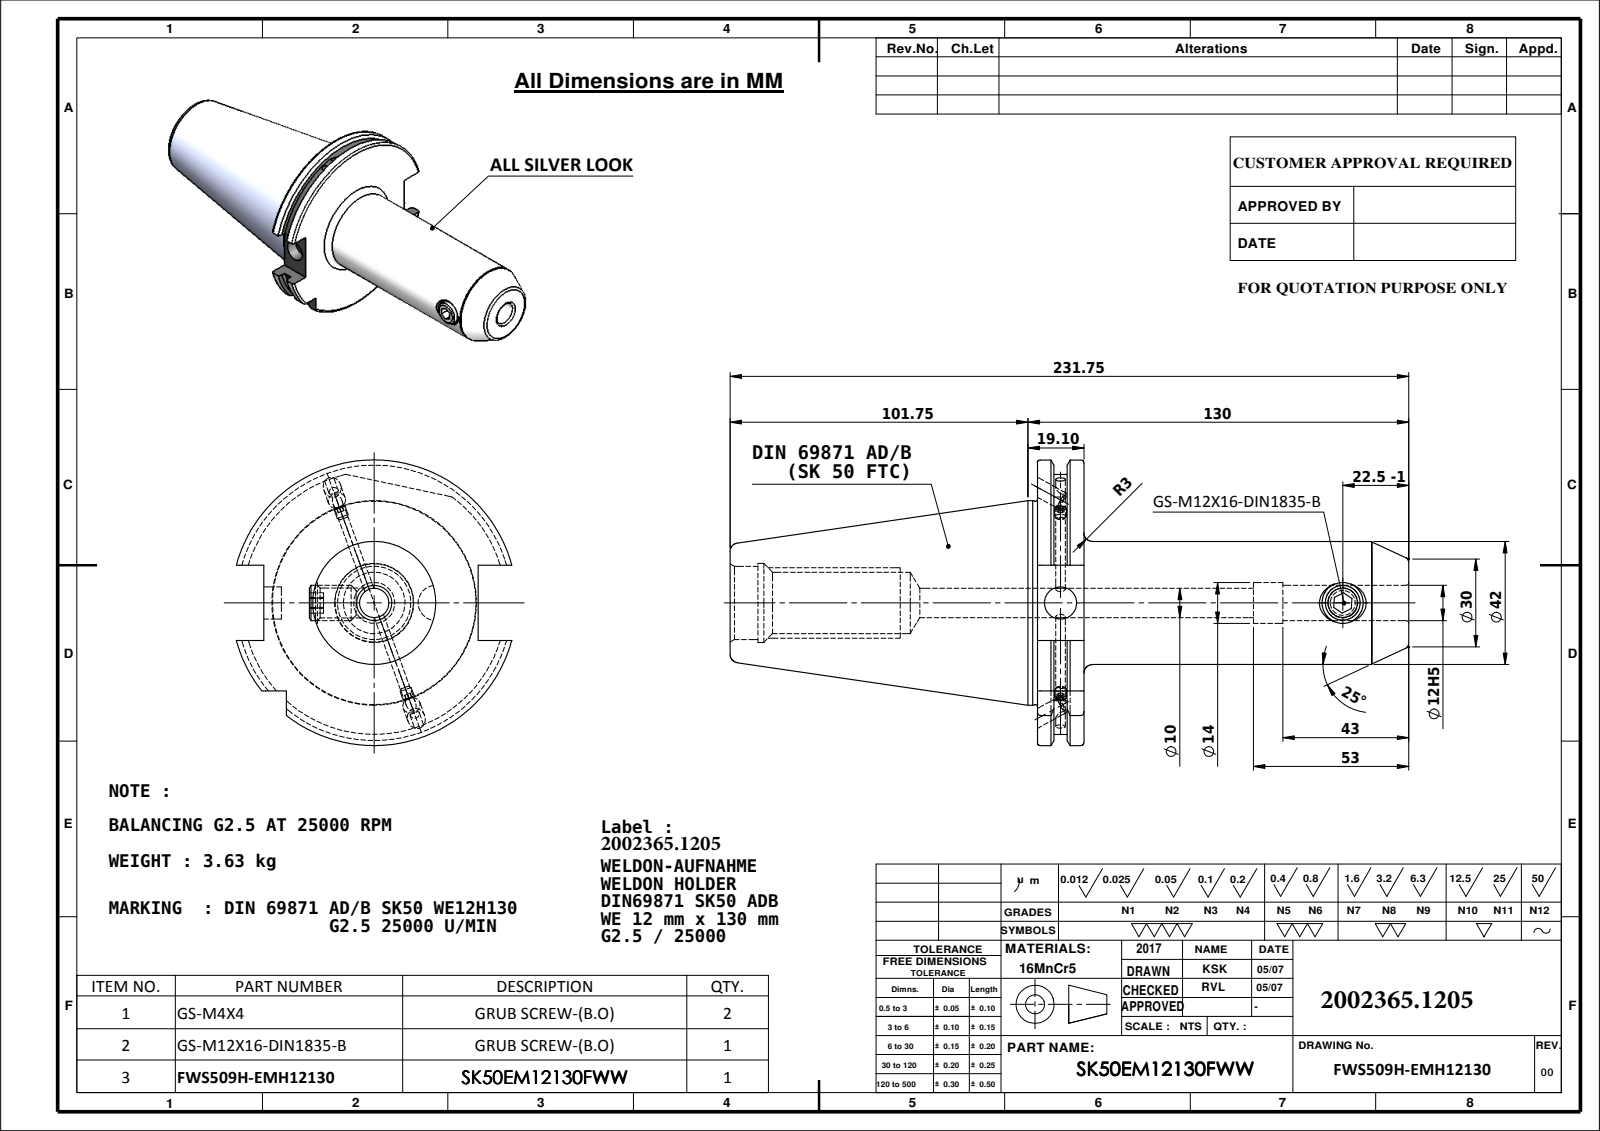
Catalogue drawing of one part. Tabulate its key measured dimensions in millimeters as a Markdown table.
| quantity | value |
| --- | --- |
| part name | SK50EM12130FWW; 91506-WE712130; Copy of M4X4_DIN 913 - M4 x 4-N; M12X16_ISO 4026 - M12 x 12-N |
| STEP written by | SolidWorks 2009 (CONFIG_CONTROL_DESIGN) |
| units | millimeters |
| bodies | 4 solids, 168 faces (53 planar, 55 cylindrical, 60 other) |
| overall size | 231.75 × 97.5 × 94.05 |
| volume | 471 326 mm³ |
| surface area | 62 419 mm² |
| round holes (diameter × count) | 6 × 2, 14 × 2, 3.3 × 1, 10 × 1, 10.2 × 1, 11 × 1, 12 × 1, 21 × 1, 25 × 1, 27 × 1 |
| round bosses / shafts (diameter × count) | 4 × 2, 69.85 × 1, 69.45 × 1, 42 × 1, 12 × 1 |
| partial cylindrical surfaces (radius × count) | 44.9 × 1, 48.75 × 1 |
| main face-to-face distances | 15.9, 10.15, 5.75, 5.66, 4.49, 10.24, 126.8, 121.14, 116.65, 110.9 |
| hole center spacings | 96.4 |
